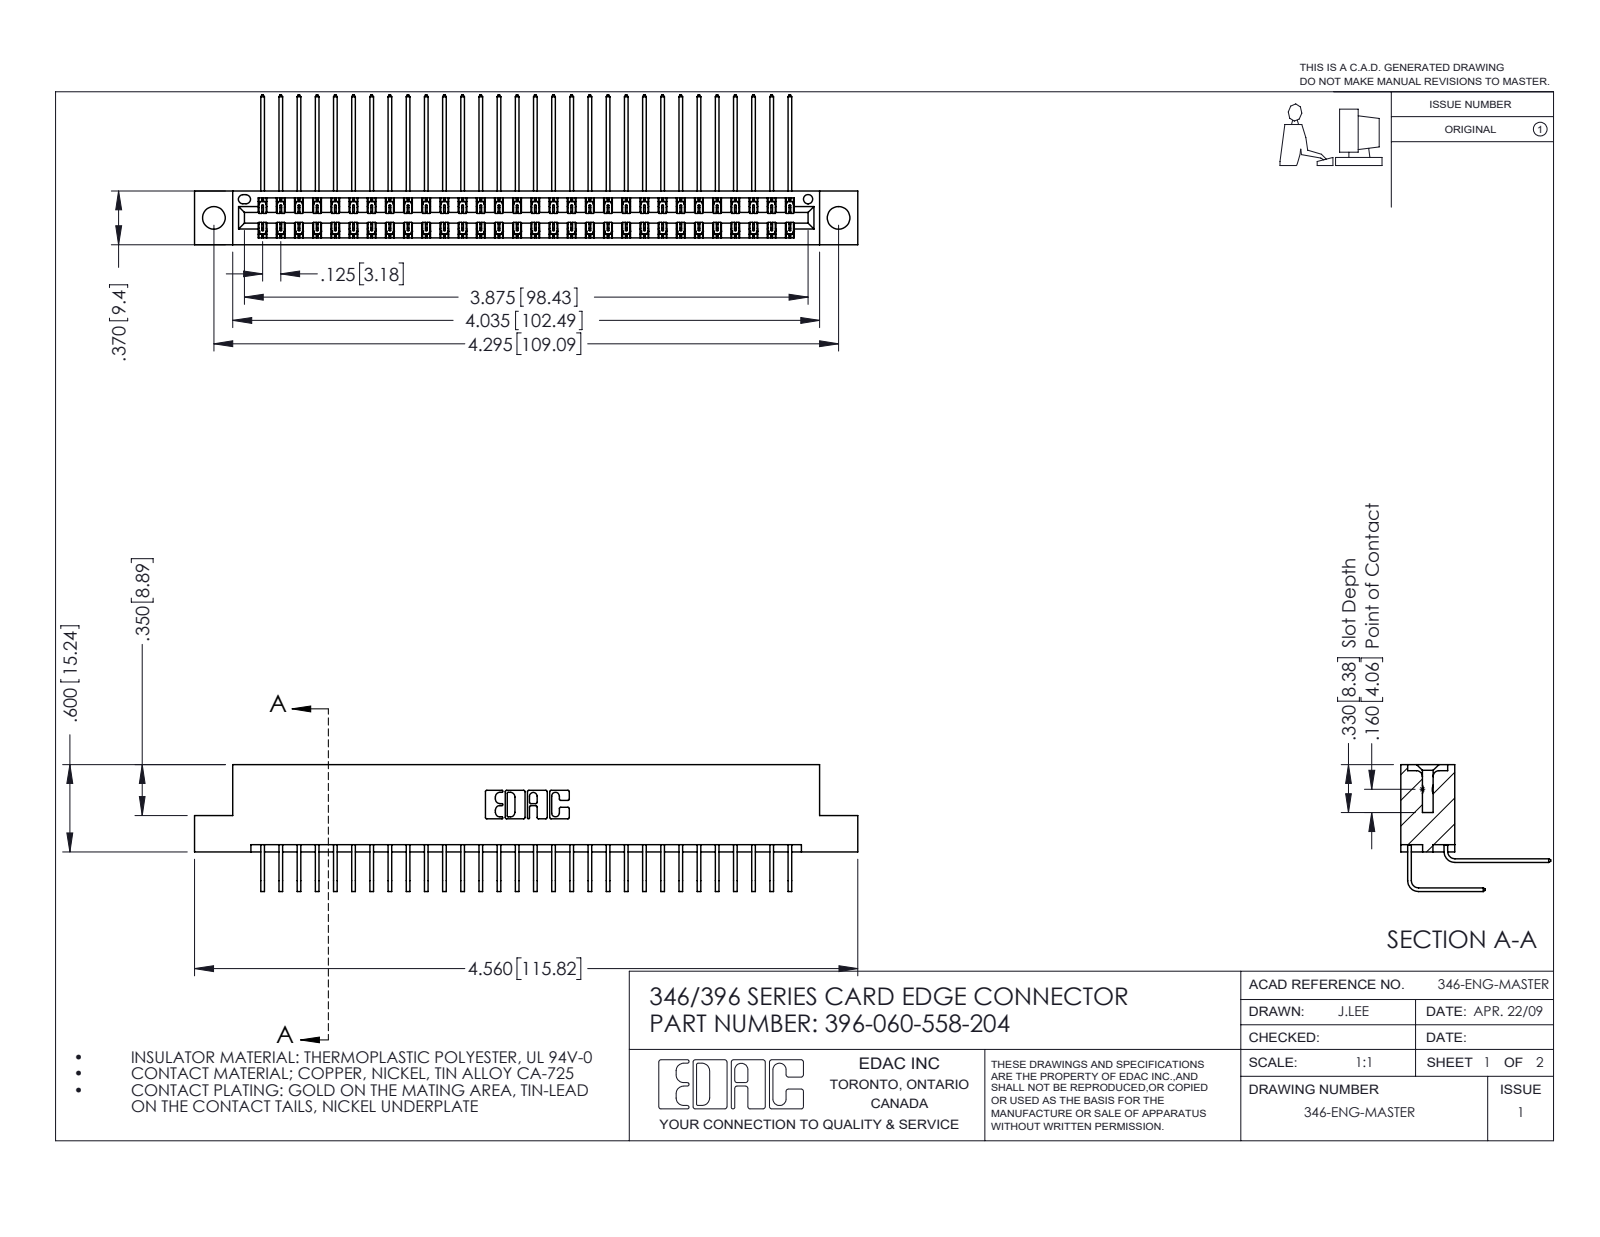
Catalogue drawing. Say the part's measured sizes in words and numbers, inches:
The part is named "396-060-558-204; 345-292-001_558 Tail - 2; 345-292-001_558 559 Tail - 1; 346 Part_Flush Mounting Lugs - 0.156 Dia-TH". Its 3-D file was written by "SolidWorks 2016 (CONFIG_CONTROL_DESIGN)". It is 61 solids with 3362 faces: 2296 planar, 1066 cylindrical and 0 other. Overall it measures 4.56 by 1.03 by 0.873 inches. Its volume is 0.699 cubic inches and its surface area 26.41 square inches. Round holes: 2 of diameter 0.156, 1 of diameter 0.064. Partial cylindrical surfaces (rounded edges, fillets, slot ends): 90 of radius 0.006, 22 of radius 0.01, 6 of radius 0.007, 6 of radius 0.031, 3 of radius 0.026, 2 of radius 0.014, 2 of radius 0.022, 2 of radius 0.024. The main face-to-face distances are 0.322, 0.048, 0.025, 0.25, 0.37, 0.298, 0.072, 0.275, 0.148, 0.222. The hole center spacings are 0.246, 4.087, 4.295.
